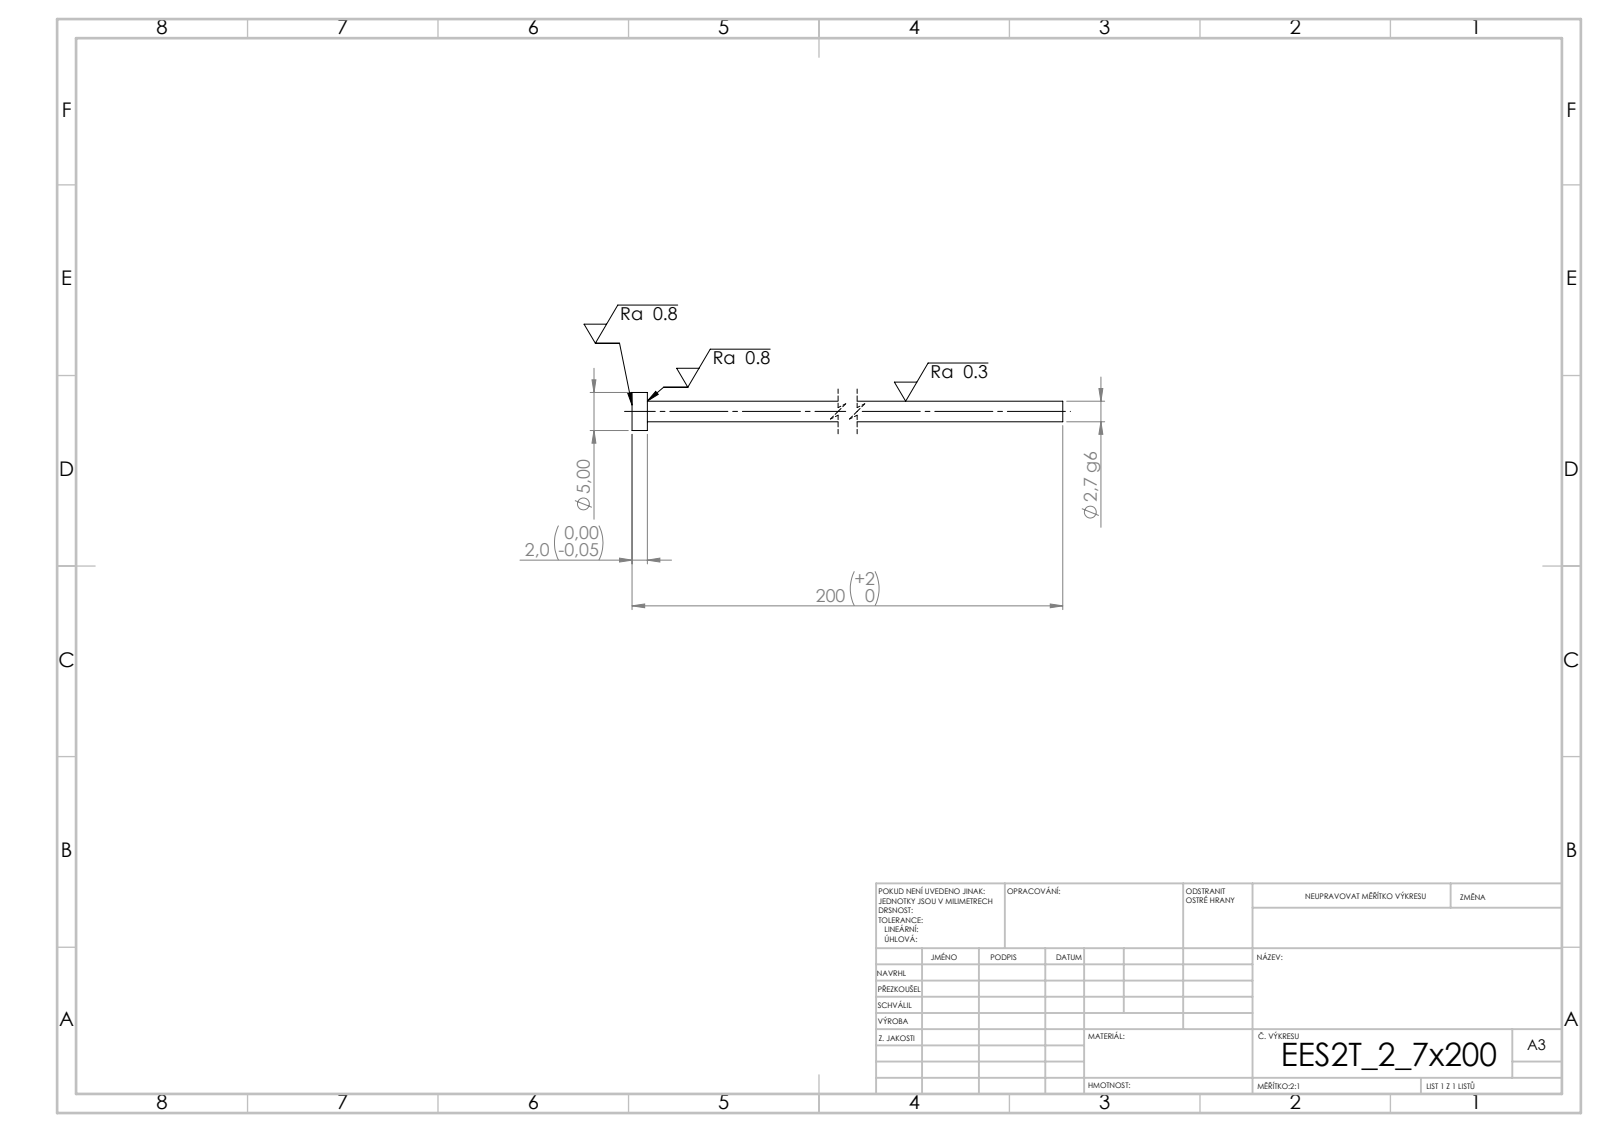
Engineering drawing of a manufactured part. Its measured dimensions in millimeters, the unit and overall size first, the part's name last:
Units: millimetres
Overall size (bounding box): 200 × 5 × 5
Round bosses / shafts (diameter × count): ⌀5 ×1, ⌀2.7 ×1
Main face-to-face distances: 2, 200, 198
Volume: 1 173 mm³ · Surface area: 1 750 mm²
Bodies: 1 solid, 7 faces (3 planar, 4 cylindrical, 0 other)
STEP written by: SolidWorks 2019 (CONFIG_CONTROL_DESIGN)
